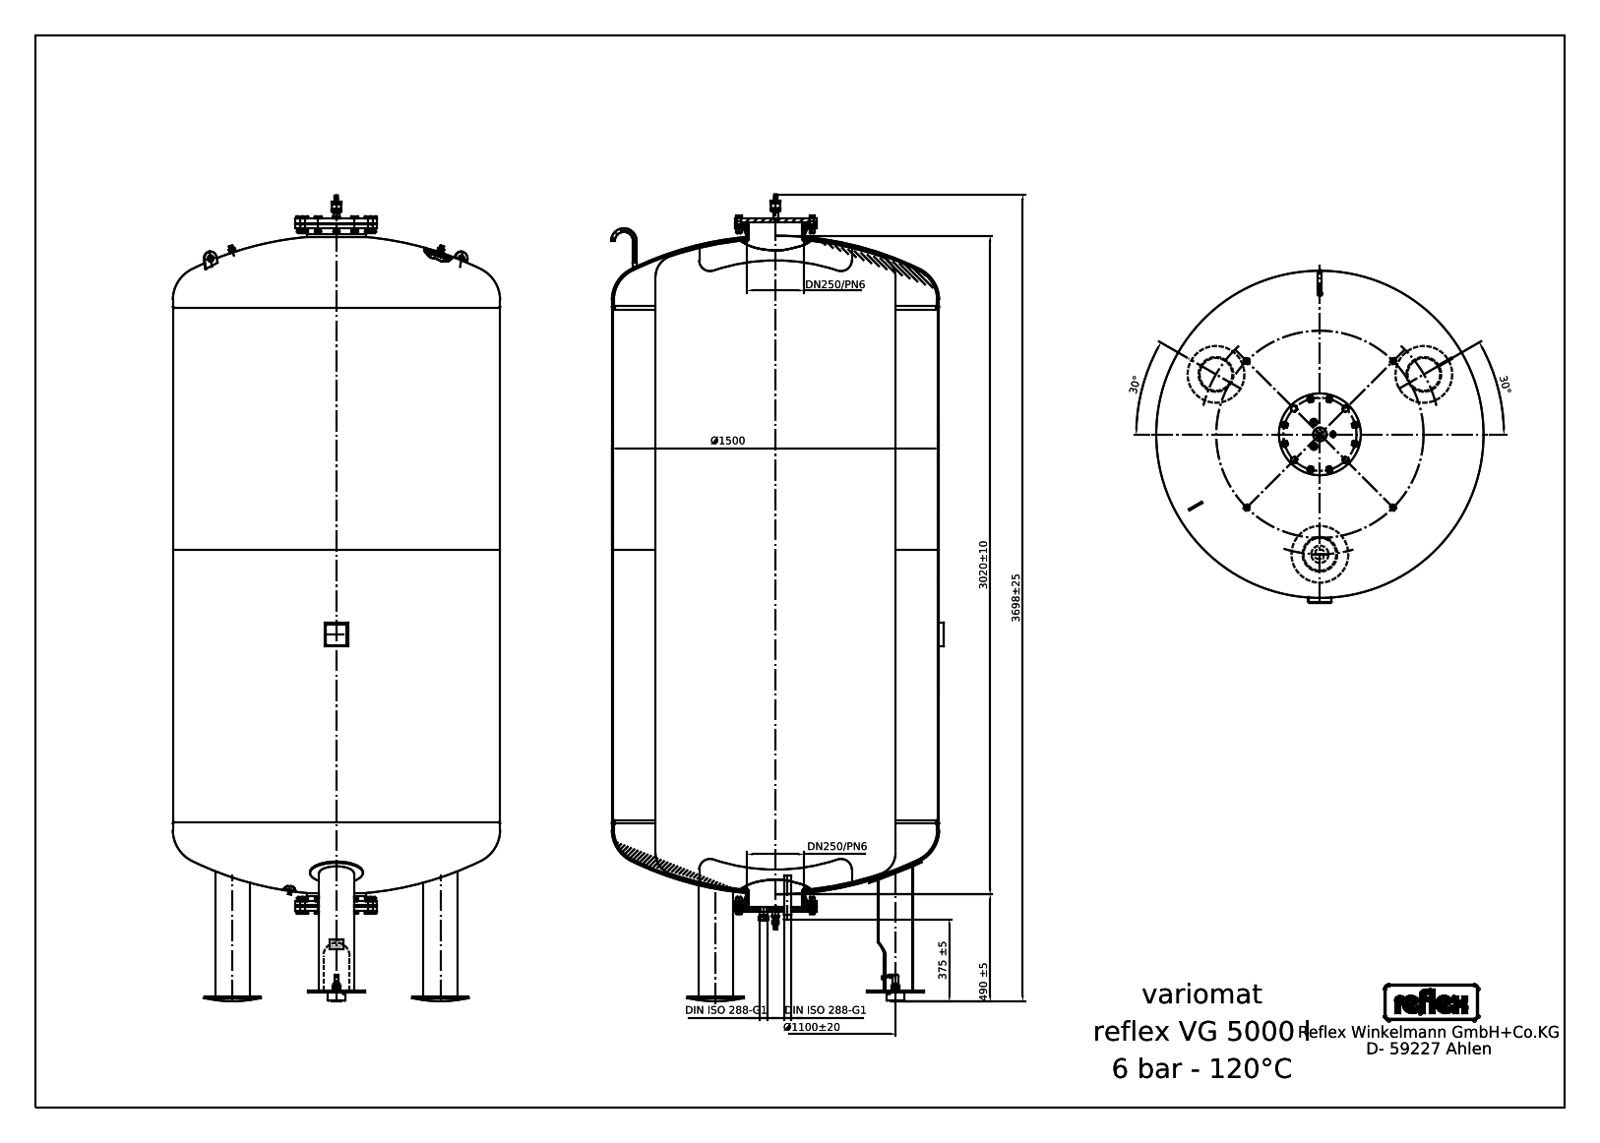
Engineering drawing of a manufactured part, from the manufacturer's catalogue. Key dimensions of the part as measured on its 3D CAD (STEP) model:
STEP written by: Mechanical Desktop 2008 (CONFIG_CONTROL_DESIGN)
Units: millimetres
Bodies: 30 solids, 842 faces (499 planar, 230 cylindrical, 113 other)
Overall size (bounding box): 3698 × 1500 × 1500
Volume: 5 023 000 000 mm³ · Surface area: 25 470 000 mm²
Round holes (diameter × count): ⌀8 ×1, ⌀20 ×1, ⌀30 ×1, ⌀150 ×1, ⌀260.4 ×1
Round bosses / shafts (diameter × count): ⌀16 ×20, ⌀159 ×3, ⌀33.7 ×2, ⌀16.6 ×2, ⌀12 ×2, ⌀1500 ×1, ⌀375 ×1, ⌀318 ×1
Partial cylindrical surfaces — rounded edges, fillets, slot ends (radius × count): R2 ×8, R8.44 ×4, R3.38 ×3, R5.76 ×2, R10.12 ×2, R13.91 ×2, R14.1 ×2, R19.06 ×2
Main face-to-face distances: 2360, 22, 389, 3155, 406, 2766, 2749, 3177, 2771, 411
Hole centre spacings: 550
